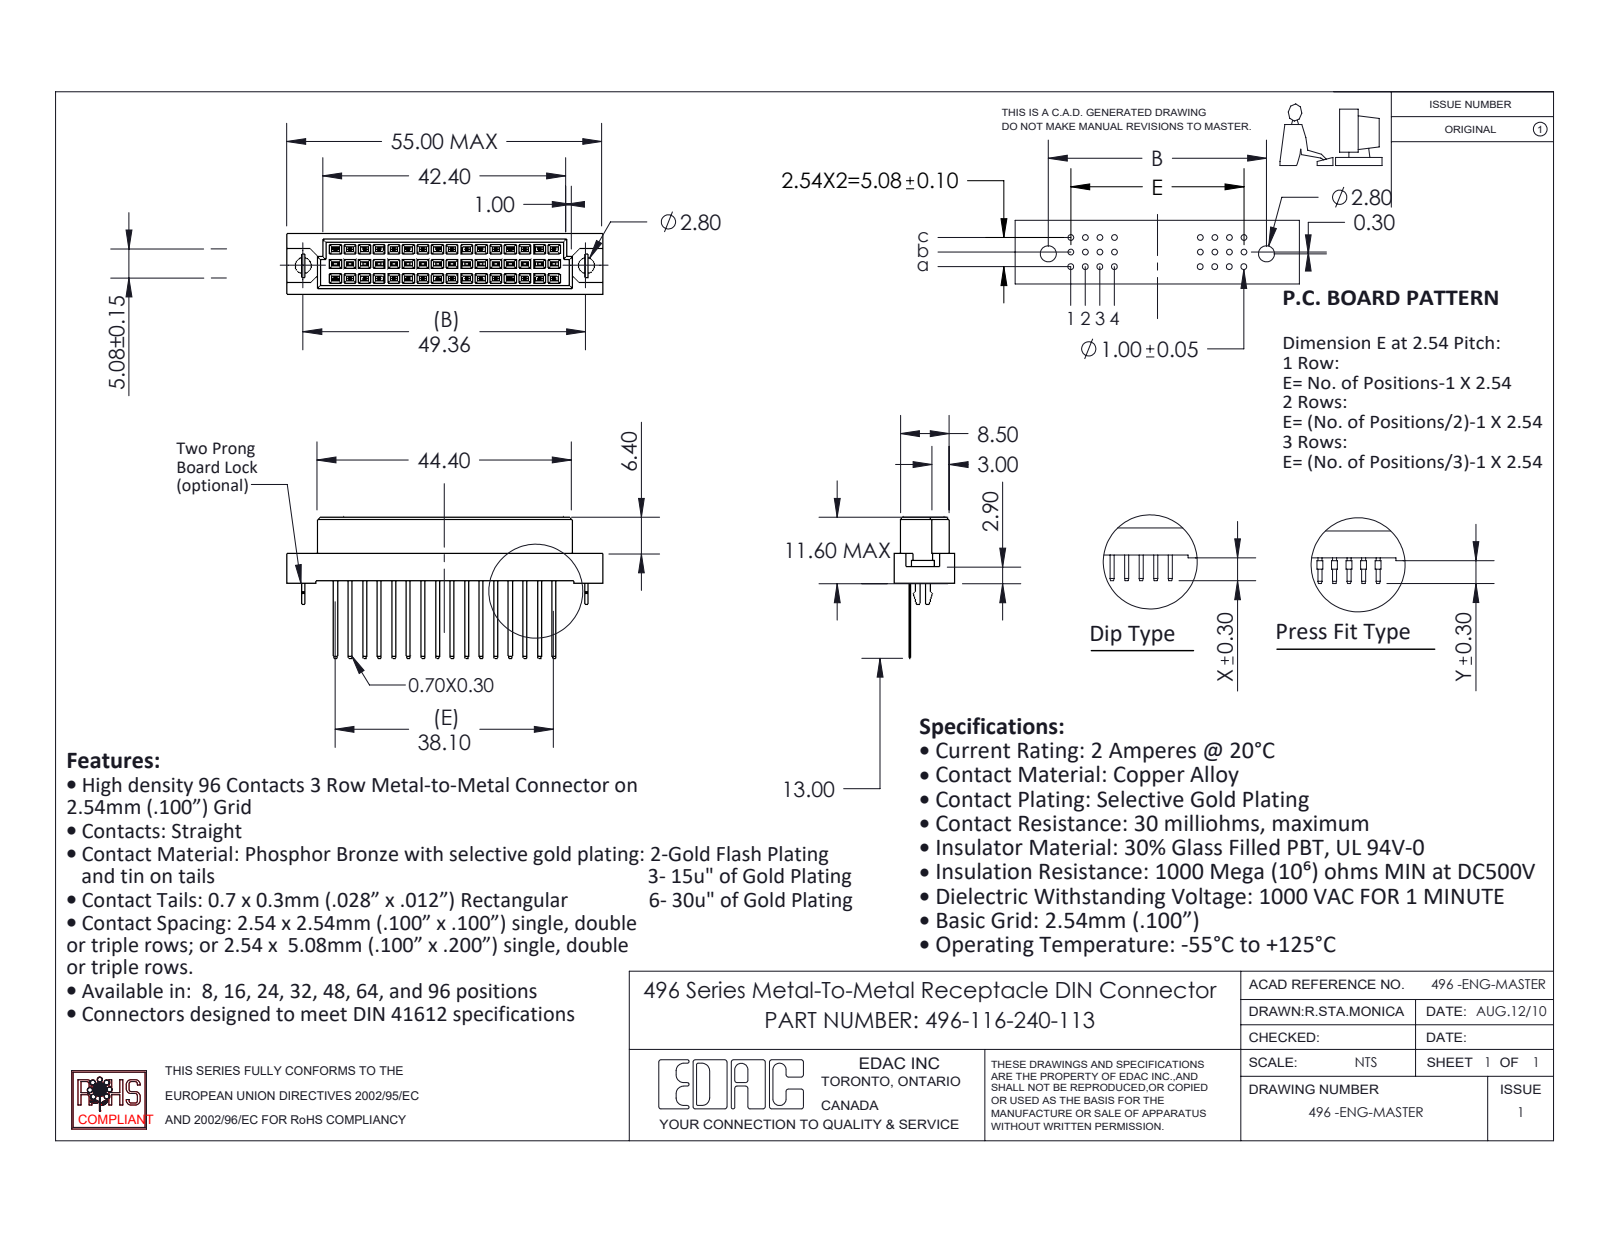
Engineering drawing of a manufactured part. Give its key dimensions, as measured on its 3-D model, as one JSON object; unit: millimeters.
{"part_name": "496 Part_48; 496-290_40; 496 Bore-lock; 496-116-240-113", "step_written_by": "SolidWorks 2020 (CONFIG_CONTROL_DESIGN)", "units": "millimeters", "bodies": {"solids": 19, "faces": 862, "planar": 856, "cylindrical": 6, "other": 0}, "overall_size": [55, 24.6, 10.6], "volume_mm3": 4671, "surface_area_mm2": 4889, "round_holes": [[2.8, 2]], "partial_cylinders_radius": [[0.53, 1]], "face_to_face_distances": [2.54, 1.05, 9.55, 5.08, 0.81, 1.56, 1.86, 2.61, 2.91, 7.69], "hole_center_spacings": [49.36]}
